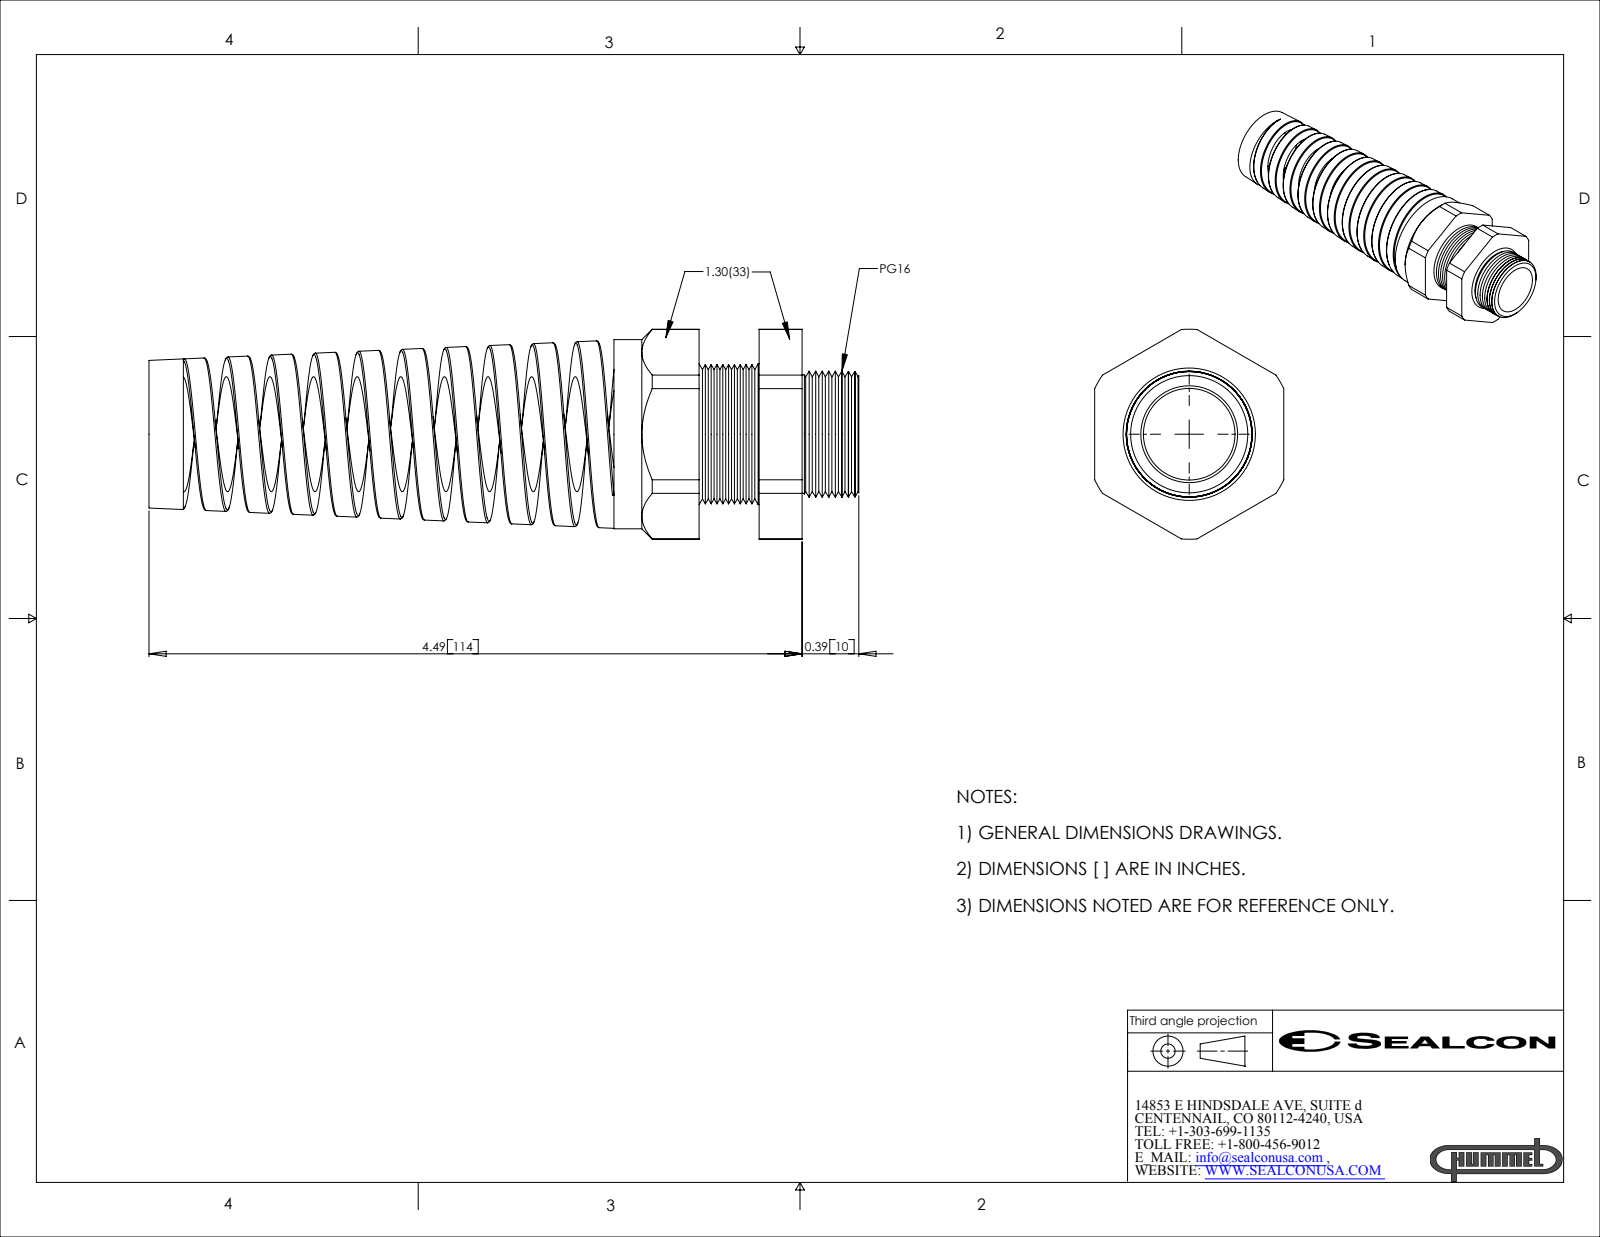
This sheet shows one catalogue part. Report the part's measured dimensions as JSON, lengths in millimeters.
{"part_name": "CF16GR-GY", "step_written_by": "SolidWorks 2007 (CONFIG_CONTROL_DESIGN)", "units": "millimeters", "bodies": {"solids": 2, "faces": 193, "planar": 24, "cylindrical": 45, "other": 124}, "overall_size": [124, 36.7, 33], "volume_mm3": 35000, "surface_area_mm2": 25810, "round_holes": [[16, 1], [20.1, 1]], "round_bosses_or_shafts": [[33, 1], [24.6, 1]], "partial_cylinders_radius": [[10.3, 1], [18.3, 1]], "face_to_face_distances": [33, 18, 10.5, 7.5, 14.9, 25.3, 32.9, 81.2, 96.1, 106.6]}
